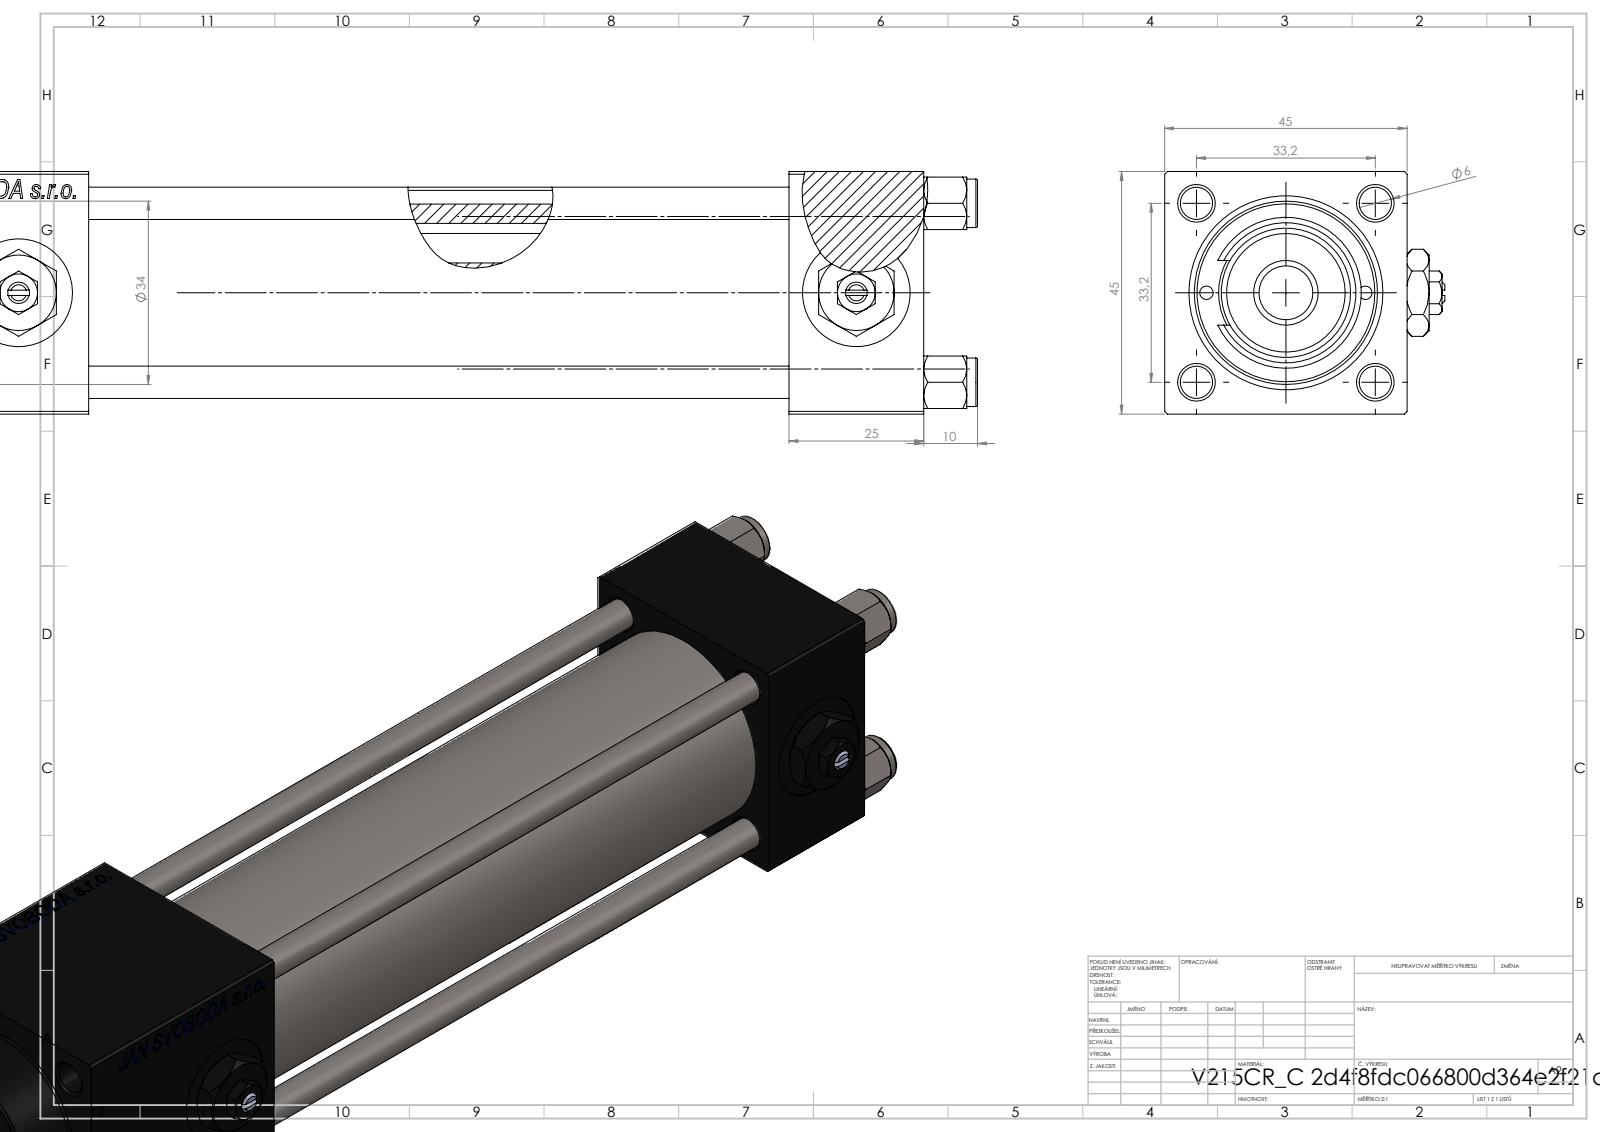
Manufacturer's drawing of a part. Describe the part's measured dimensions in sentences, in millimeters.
The part is named "V215CR_C_TYCINKA; NUT_M5_C; Zatka_pro_OIL_PORT; V215CR_C_Body (+4 more)". Its 3-D file was written by "SolidWorks 2019 (CONFIG_CONTROL_DESIGN)". It is 15 solids with 1339 faces: 602 planar, 115 cylindrical and 622 other. Overall it measures 299 by 52 by 45 millimeters. Its volume is 291 866 cubic millimeters and its surface area 109 686 square millimeters. Round holes: 4 of diameter 6, 2 of diameter 2.5, 2 of diameter 7, 2 of diameter 13.16, 2 of diameter 20, 1 of diameter 10.5, 1 of diameter 22, 1 of diameter 24, 1 of diameter 25, 1 of diameter 32, 1 of diameter 33. Round bosses or shafts: 4 of diameter 9, 1 of diameter 38, 1 of diameter 34, 1 of diameter 28, 1 of diameter 18, 1 of diameter 12, 1 of diameter 11, 1 of diameter 10. Partial cylindrical surfaces (rounded edges, fillets, slot ends): 1 of radius 9.75, 1 of radius 10.5. The main face-to-face distances are 45, 25, 203, 155, 130, 178, 44.8, 13, 48, 174.3. The hole center spacings are 16.7, 23.48, 33.2, 35.47, 14.75, 46.95, 29.5, 155.5.
